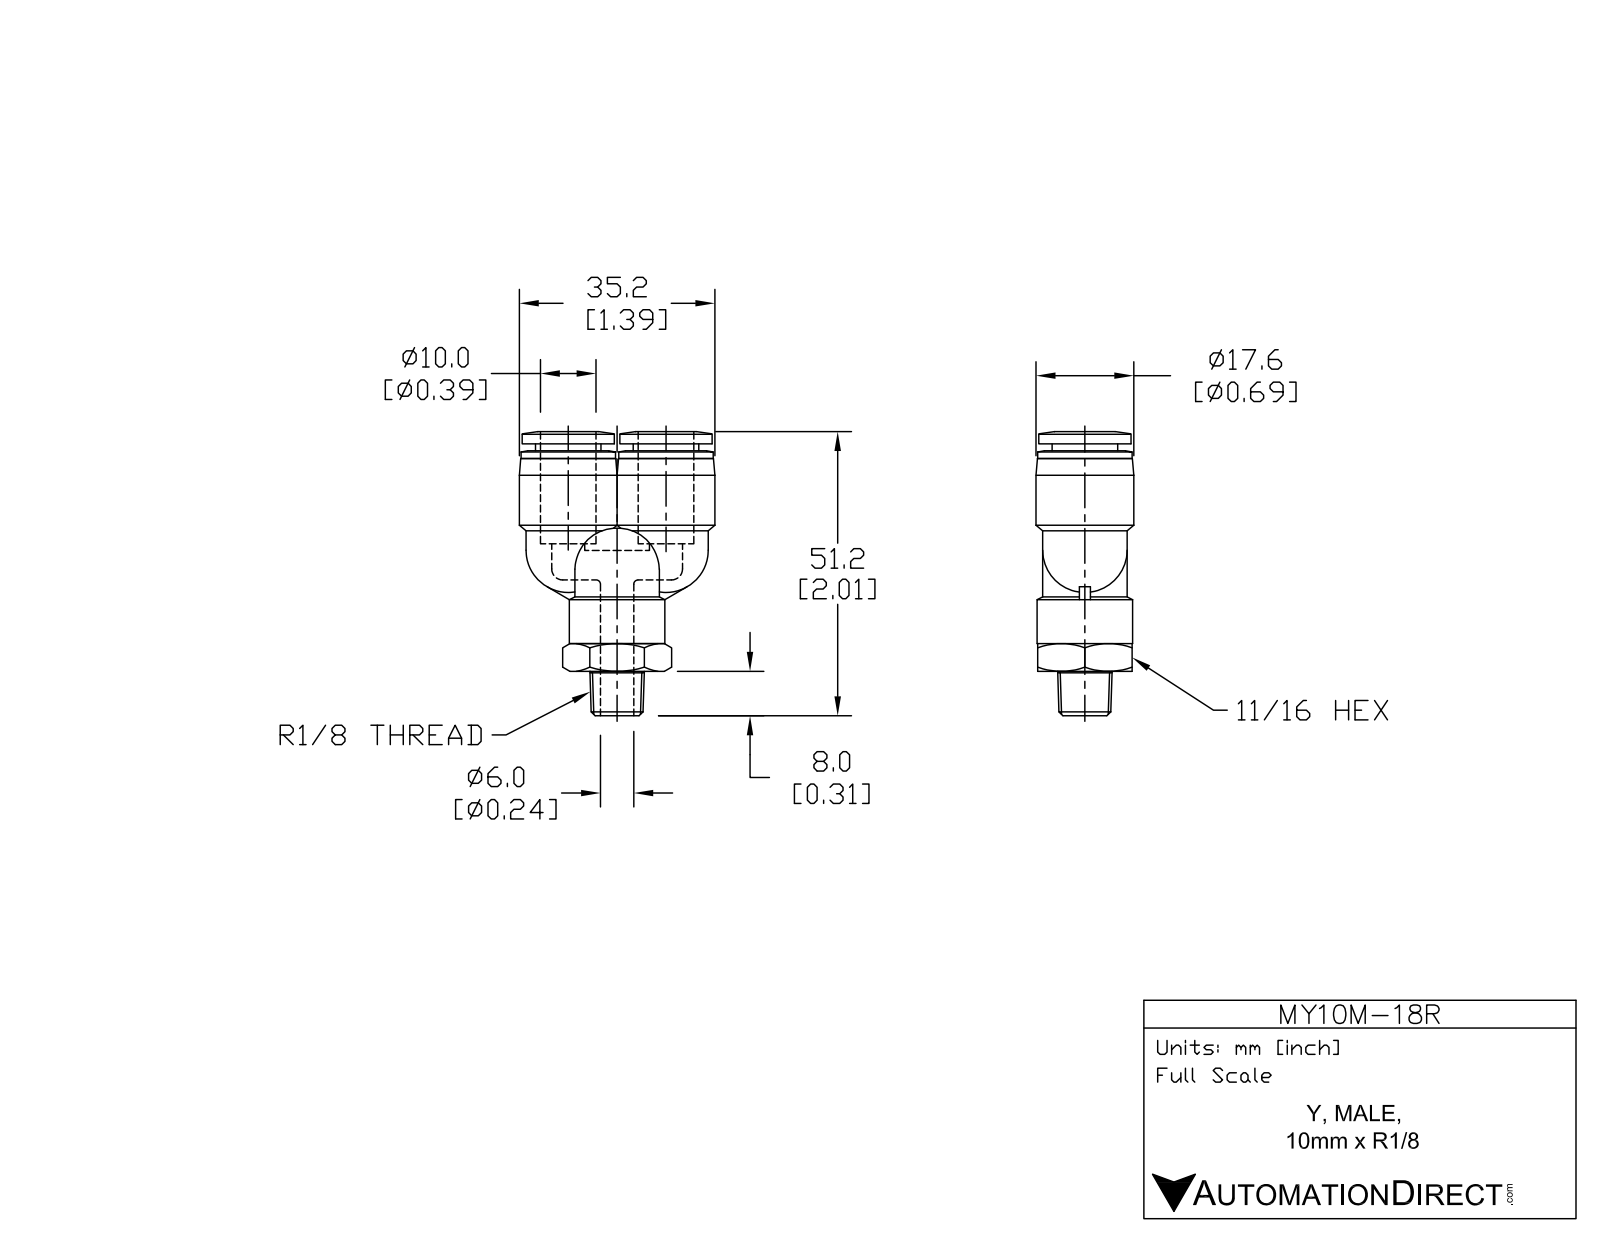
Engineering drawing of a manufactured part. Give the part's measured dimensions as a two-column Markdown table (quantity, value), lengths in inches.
| quantity | value |
| --- | --- |
| part name | MY10M-18R |
| STEP written by | SolidWorks 2015 (AUTOMOTIVE_DESIGN) |
| units | inches |
| bodies | 1 solid, 110 faces (24 planar, 35 cylindrical, 51 other) |
| overall size | 2.018 × 1.386 × 0.693 |
| volume | 0.689 in³ |
| surface area | 11.05 in² |
| round holes (diameter × count) | 0.236 × 4, 0.406 × 2 |
| round bosses / shafts (diameter × count) | 0.598 × 3, 0.693 × 2, 0.669 × 2, 0.654 × 2, 0.465 × 2, 0.677 × 1 |
| main face-to-face distances | 1.616, 0.669, 1.567, 0.049, 0.904, 0.663, 0.713, 0.315, 1.219, 1.882 |
| hole center spacings | 0.346, 0.693 |
